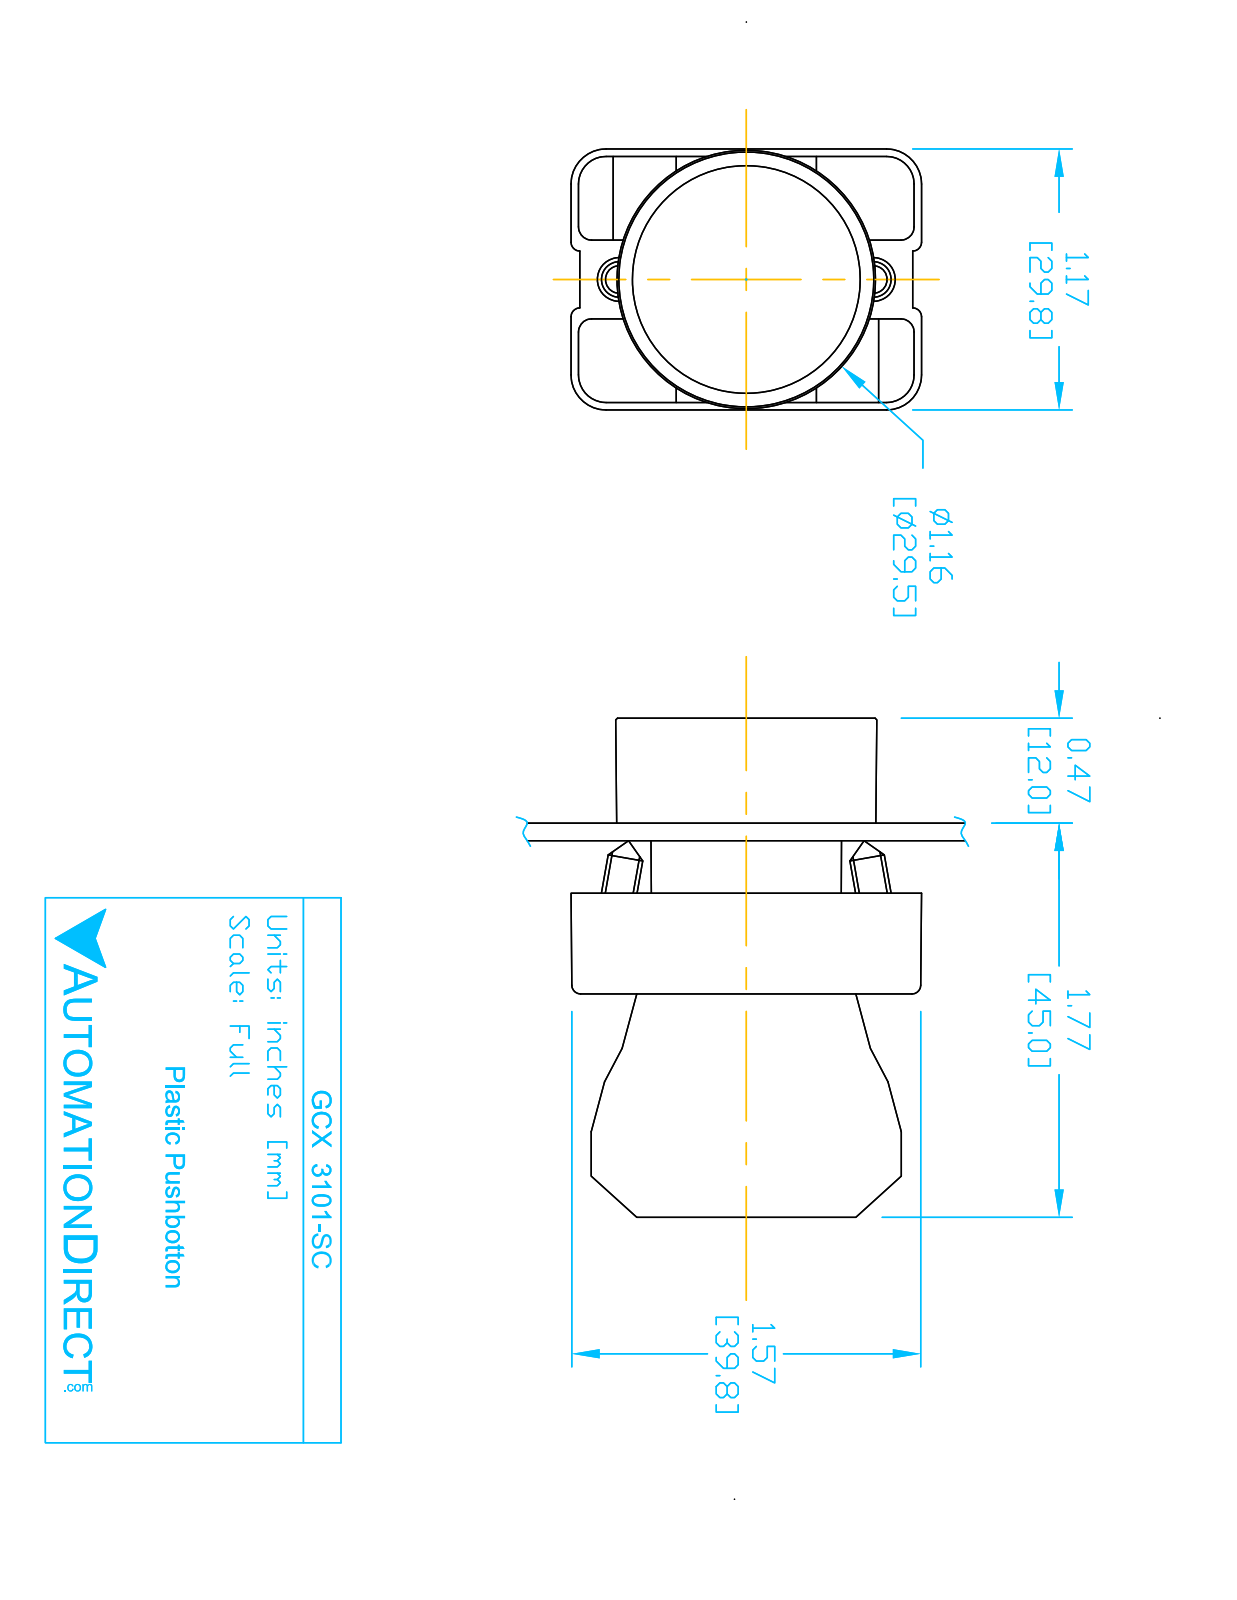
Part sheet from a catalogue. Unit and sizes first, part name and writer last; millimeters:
Units: millimetres
Overall size (bounding box): 40.2 × 35.7 × 29.9
Round holes (diameter × count): ⌀3.1 ×2, ⌀3.3 ×2, ⌀5 ×1, ⌀22.3 ×1, ⌀22.6 ×1, ⌀26 ×1
Round bosses / shafts (diameter × count): ⌀4 ×2, ⌀29.8 ×1, ⌀25.5 ×1, ⌀24 ×1, ⌀21.7 ×1, ⌀19.8 ×1
Partial cylindrical surfaces — rounded edges, fillets, slot ends (radius × count): R1.5 ×24, R1 ×12, R3.1 ×12, R4 ×12, R1 ×4, R3.3 ×2, R10 ×1, R10.1 ×1
Main face-to-face distances: 0.8, 18.3, 30.3, 12, 0.8, 17.5, 29.5, 3.1, 2.3, 15.2
Volume: 17 860 mm³ · Surface area: 13 170 mm²
Bodies: 5 solids, 288 faces (147 planar, 118 cylindrical, 23 other)
Part name (STEP PRODUCT): GCX3101-SC; ECX3029-2; GCX3101 OPERATOR
STEP written by: SolidWorks 2016 (AUTOMOTIVE_DESIGN)
